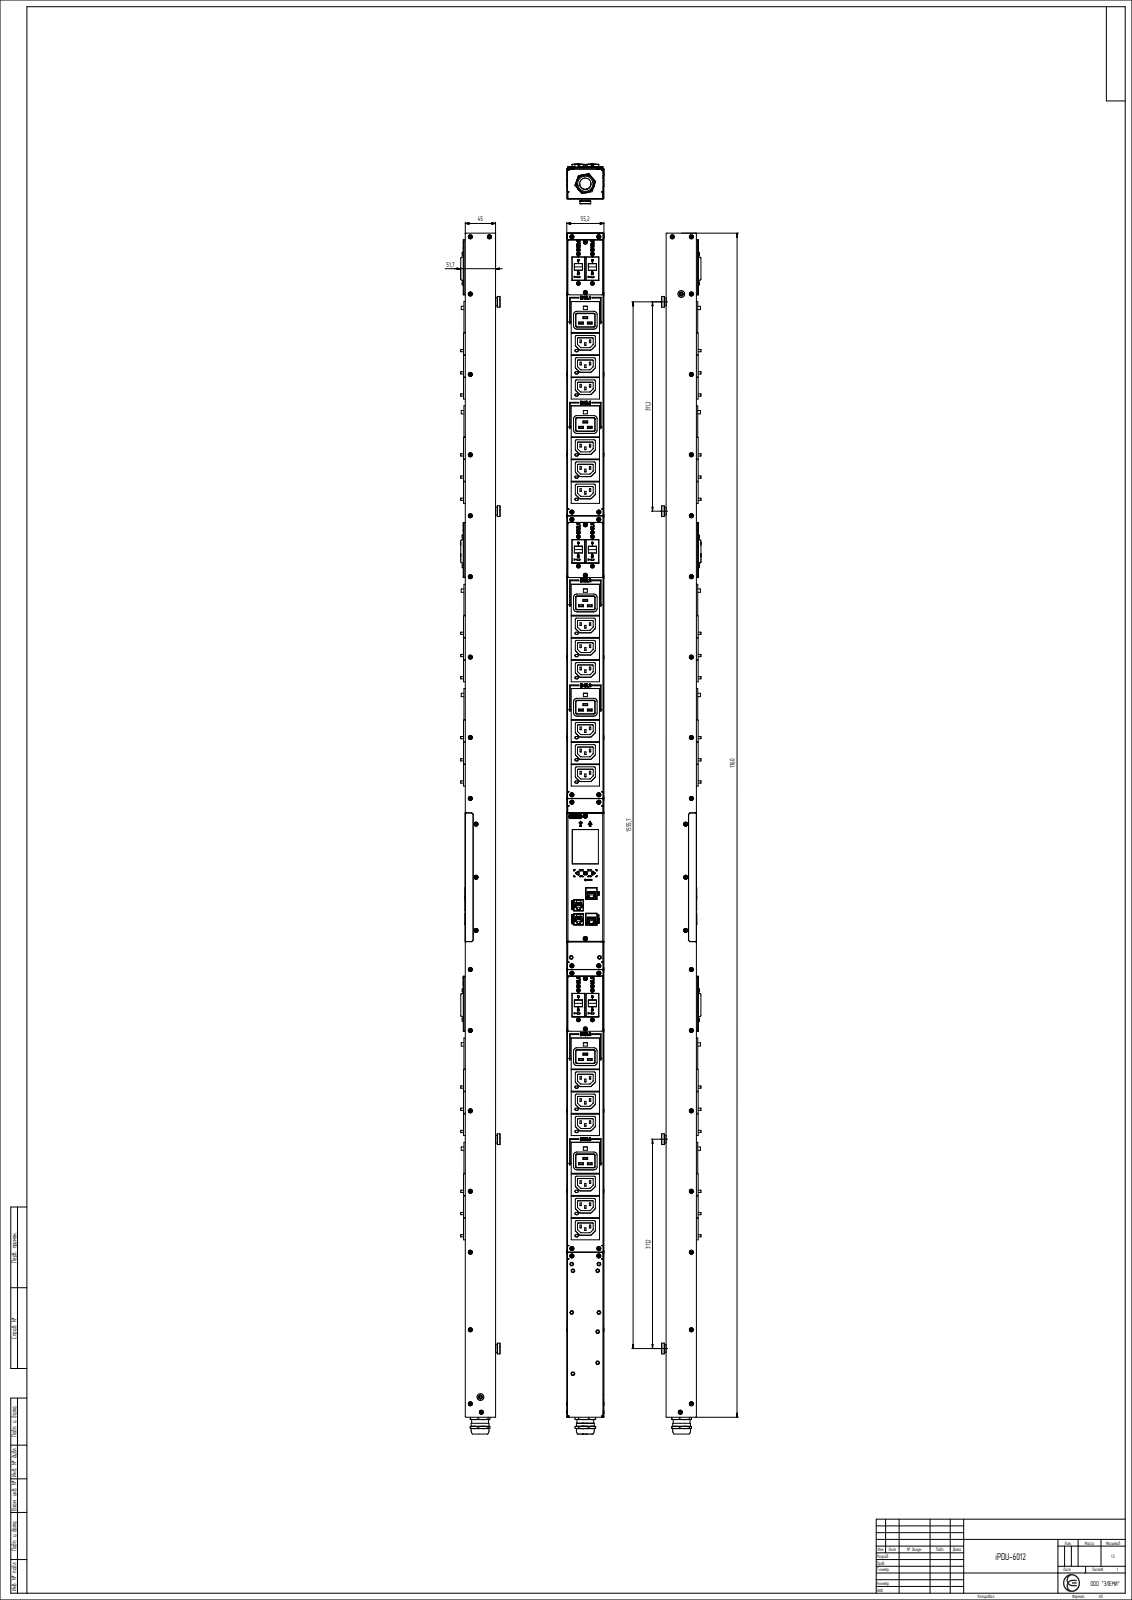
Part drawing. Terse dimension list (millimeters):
name: iPDU-6012
written by: C3D Toolkit (AUTOMOTIVE_DESIGN)
unit: mm
bodies: 163 solids, 3176 faces (2106 planar, 479 cylindrical, 591 other)
size: 1785 × 55.2 × 51.72
volume: 4 502 000 mm³; area: 402 470 mm²
holes: 10× ⌀4, 2× ⌀10, 1× ⌀2.5, 1× ⌀14
bosses: 1× ⌀26.5, 1× ⌀0.82, 1× ⌀0.64
rounds: 132× R2, 108× R1, 72× R1.45, 52× R0.25, 24× R1.5, 24× R5, 20× R0.76, 4× R0.1
face distances: 55.2, 45, 47.6, 2.6, 0.4, 3, 48, 51.72, 6.72, 4.12
hole spacings: 25, 87.52, 95.94, 397.97, 406.47, 783.2, 954.48, 1331.28
